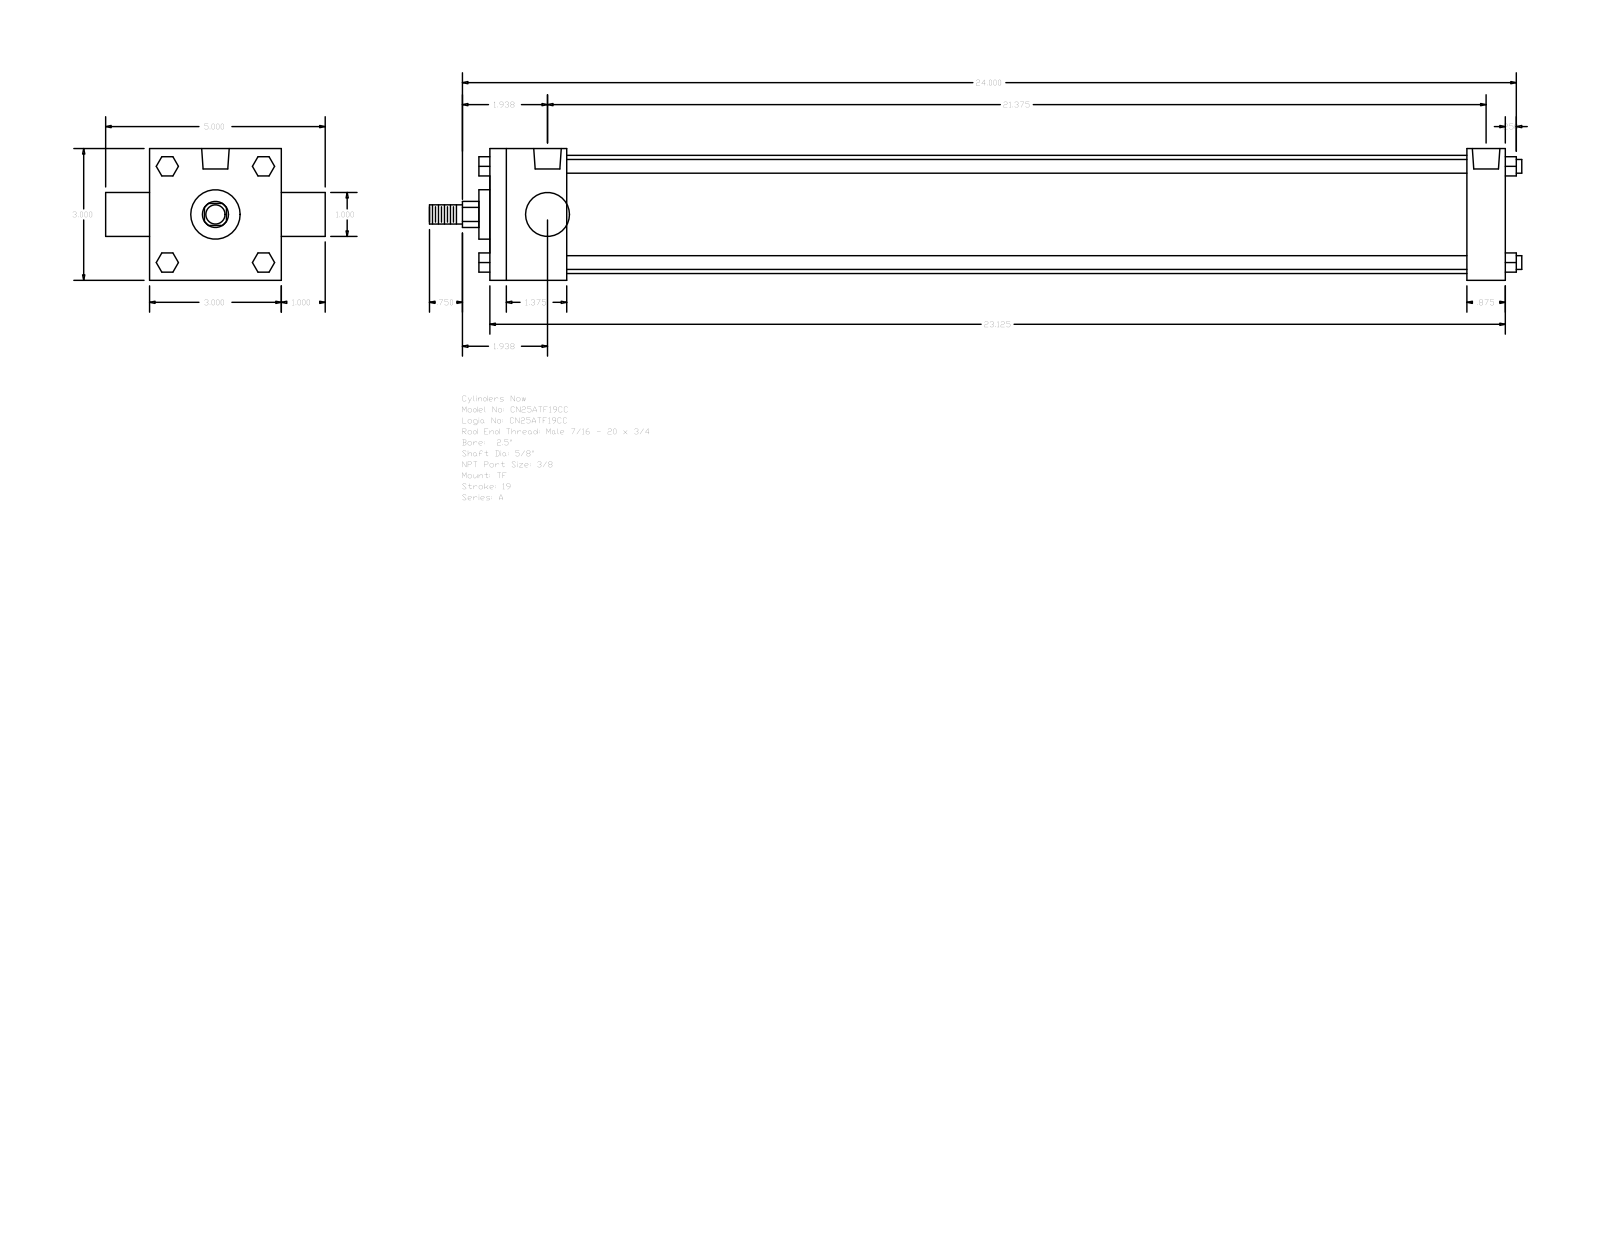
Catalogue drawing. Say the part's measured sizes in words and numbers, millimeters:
The part is named "A_TF__0250_0.625". Its 3-D file was written by "GSSL Pune (CONFIG_CONTROL_DESIGN)". It is 0 solids with 120 faces: 92 planar, 28 cylindrical and 0 other. Overall it measures 631.83 by 127 by 76.2 millimeters. Round holes: 3 of diameter 5.56, 2 of diameter 15.93. Round bosses or shafts: 4 of diameter 7.94, 1 of diameter 68.33, 1 of diameter 28.57, 1 of diameter 25.4, 1 of diameter 15.88, 1 of diameter 11.11. Partial cylindrical surfaces (rounded edges, fillets, slot ends): 1 of radius 7.54. The main face-to-face distances are 76.2, 587.37, 44.45, 565.14, 520.69, 542.92, 22.23, 25.4, 101.6, 6.35. The hole center spacings are 2.38, 545.31, 542.93, 547.69.
